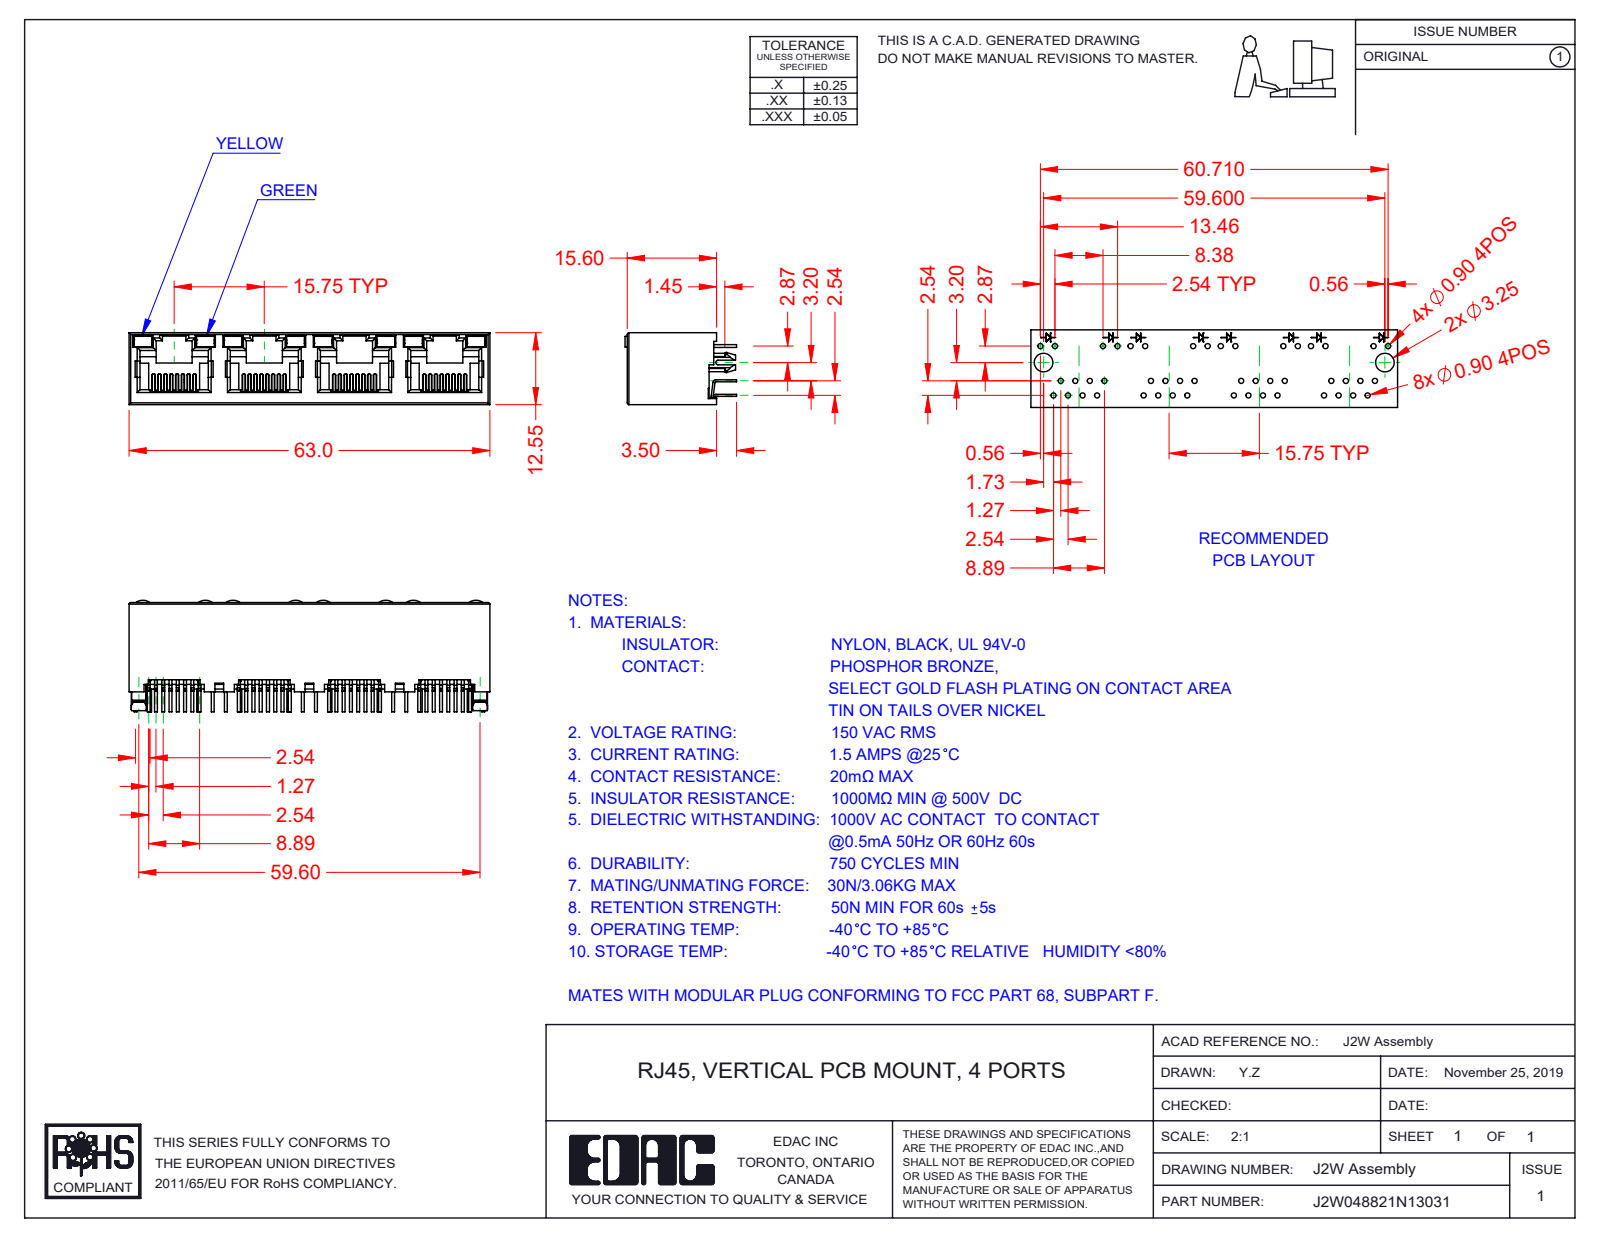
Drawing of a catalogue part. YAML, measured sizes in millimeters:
part_name: "2W LED LH_1-Yellow; 2W Insulator; 2W Contact Lock; 2W Contacts (+2 more)"
step_written_by: "SolidWorks 2020 (CONFIG_CONTROL_DESIGN)"
units: millimeters
bodies: {solids: 45, faces: 3135, planar: 2600, cylindrical: 477, other: 58}
overall_size: [63, 19.5, 12.55]
volume: 5335
surface_area: 13144
partial_cylinders:
  - {radius: 0.15, count: 64}
  - {radius: 0.2, count: 29}
  - {radius: 0.5, count: 28}
  - {radius: 0.3, count: 14}
  - {radius: 0.45, count: 8}
  - {radius: 2, count: 8}
  - {radius: 0.25, count: 2}
  - {radius: 1.5, count: 2}
face_to_face_distances: [12.55, 11.9, 0.65, 15.75, 0.36, 1.5, 0.78, 0.6, 11.3, 31.5]
